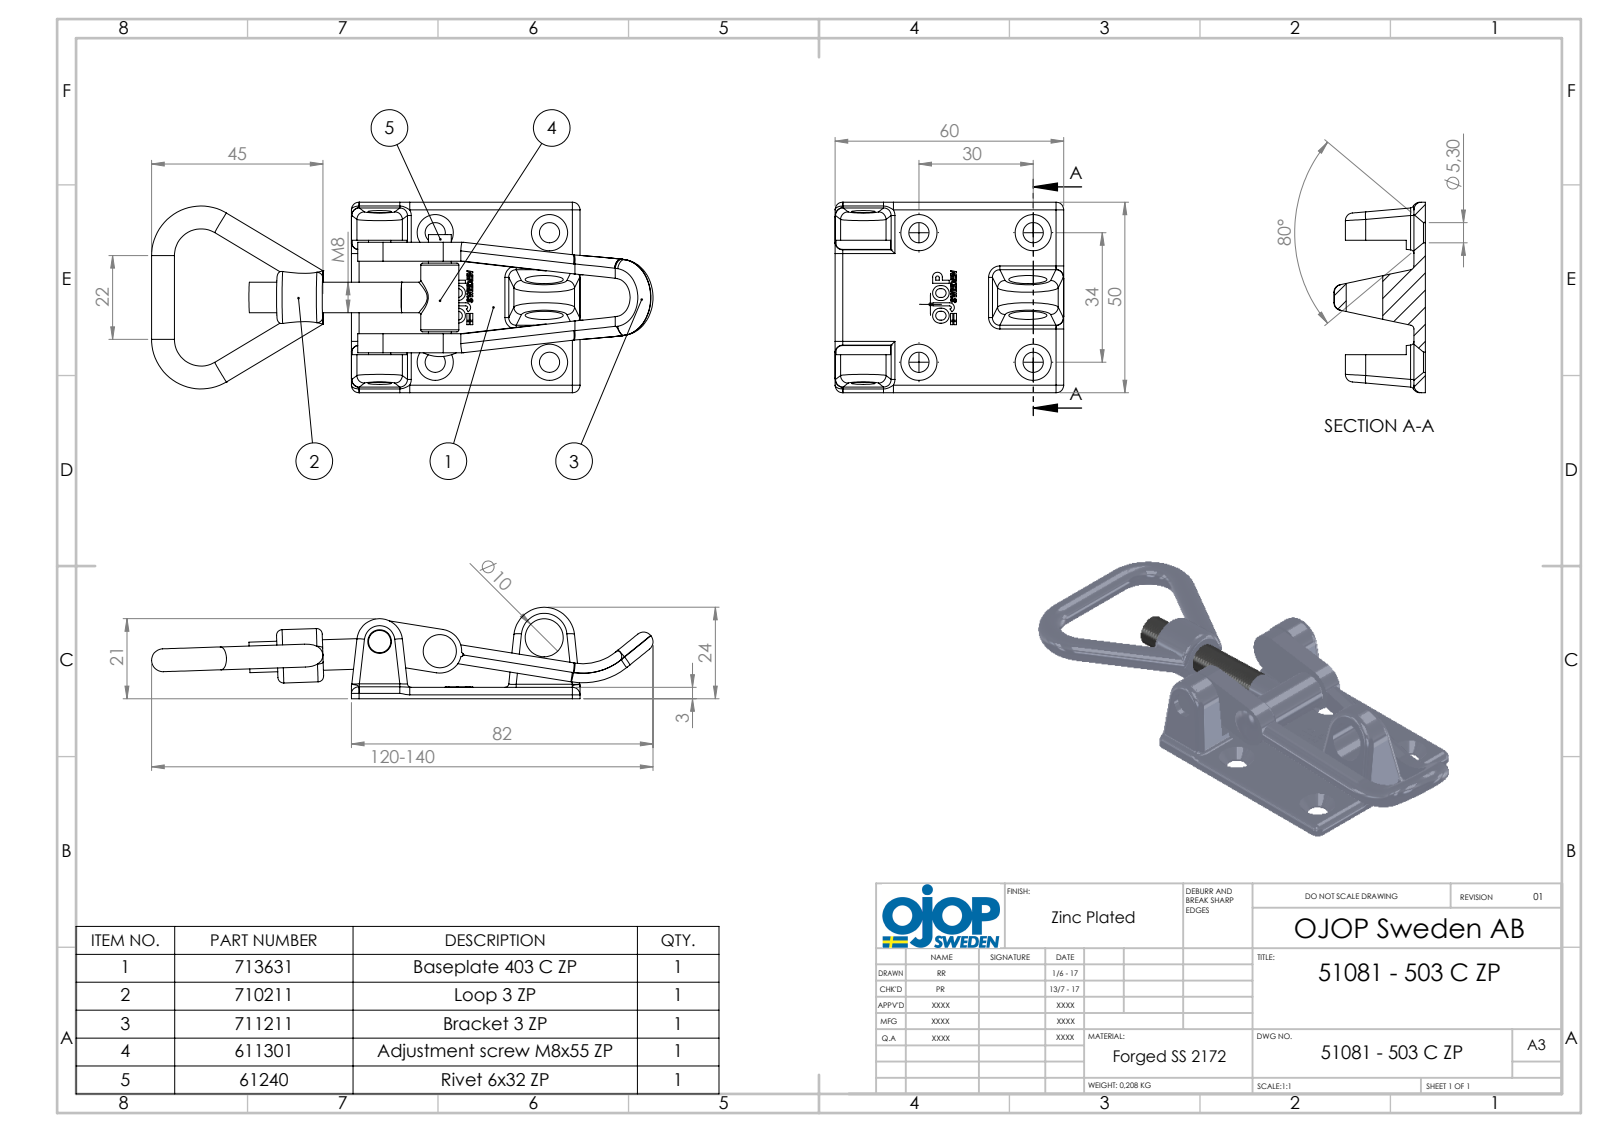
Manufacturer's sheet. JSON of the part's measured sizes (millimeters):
{"part_name": "Hålnit 6x32; Justerskruv M8; 51081 - 503 C fzb; bygel 3 (+2 more)", "step_written_by": "SolidWorks 2015 (AUTOMOTIVE_DESIGN)", "units": "millimeters", "bodies": {"solids": 5, "faces": 270, "planar": 60, "cylindrical": 105, "other": 105}, "overall_size": [141.28, 50, 24], "volume_mm3": 28528, "surface_area_mm2": 18947, "round_holes": [[5.3, 4], [6.2, 2], [3, 1], [6.3, 1], [8.1, 1], [10, 1]], "round_bosses_or_shafts": [[6, 4], [10, 1], [8.01, 1], [8, 1], [5.85, 1]], "partial_cylinders_radius": [[2, 30], [2.5, 8], [6.99, 4], [1.5, 2], [6.15, 2], [2.4, 1], [5, 1], [6, 1]], "face_to_face_distances": [3, 5, 25, 30, 20, 10, 15, 35, 40, 3.63], "hole_center_spacings": [30, 34, 45.34, 16, 27.73, 43.21]}
